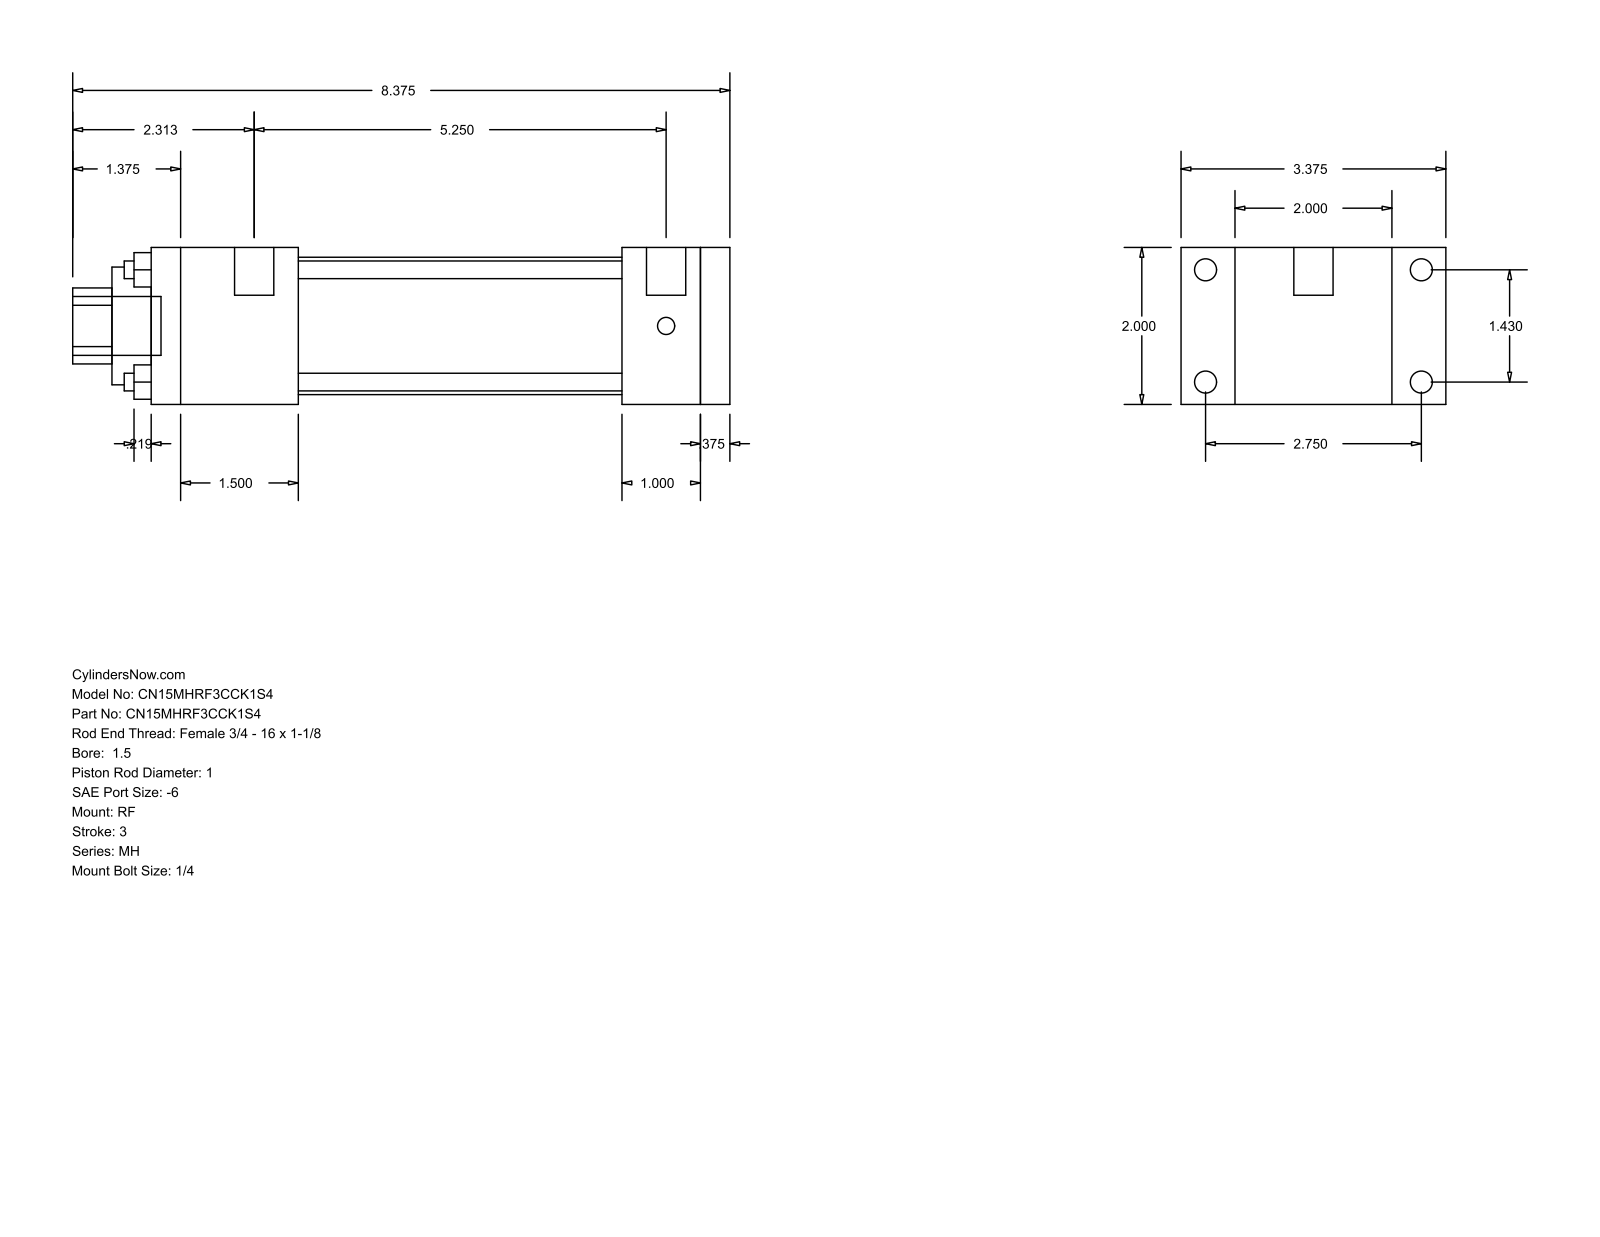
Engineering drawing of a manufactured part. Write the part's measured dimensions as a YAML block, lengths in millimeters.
part_name: "MH_RF__0150_1"
step_written_by: "GSSL Pune (CONFIG_CONTROL_DESIGN)"
units: millimeters
bodies: {solids: 0, faces: 92, planar: 64, cylindrical: 28, other: 0}
overall_size: [212.72, 85.72, 50.8]
round_holes:
  - {diameter: 5.71, count: 4}
  - {diameter: 25.4, count: 1}
  - {diameter: 38.1, count: 1}
  - {diameter: 44.45, count: 1}
round_bosses_or_shafts:
  - {diameter: 7.14, count: 4}
  - {diameter: 5.56, count: 4}
  - {diameter: 12.7, count: 2}
  - {diameter: 19.05, count: 1}
partial_cylinders:
  - {radius: 12.29, count: 1}
face_to_face_distances: [50.8, 9.52, 177.8, 25.4, 187.32, 17.46, 68.26, 152.4, 34.92, 47.63]
hole_center_spacings: [25.68, 36.32, 51.36]
